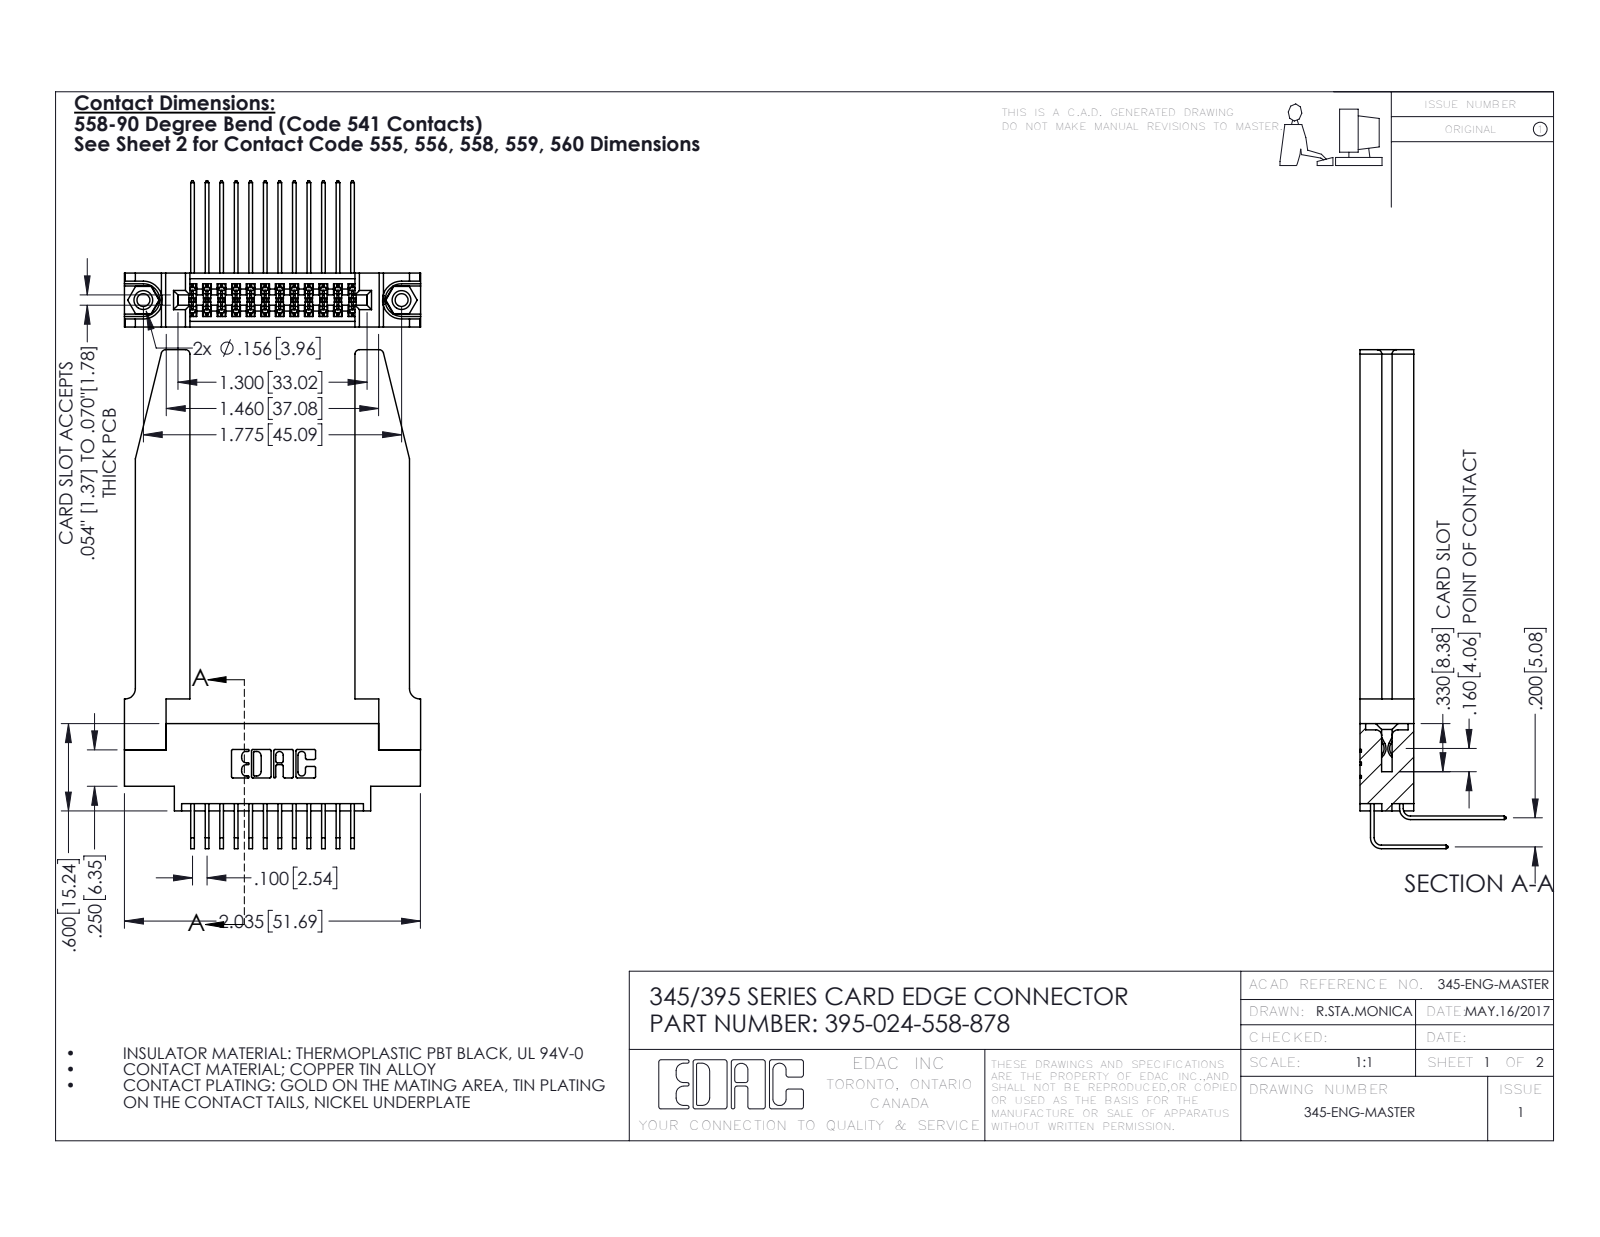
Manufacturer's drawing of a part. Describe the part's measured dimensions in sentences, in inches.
The part is named "345-220-078_345-220-078; 345 Part_0.170 Offset - 0.156 Dia-TH; 345-250-001_345-250-001-102; 345-292-001_558 Tail - 2 (+2 more)". Its 3-D file was written by "SolidWorks 2016 (CONFIG_CONTROL_DESIGN)". It is 29 solids with 1612 faces: 1066 planar, 494 cylindrical and 52 other. Overall it measures 3.429 by 2.036 by 1.005 inches. Its volume is 0.765 cubic inches and its surface area 21.86 square inches. Round holes: 2 of diameter 0.089, 2 of diameter 0.125, 2 of diameter 0.156, 1 of diameter 0.064. Round bosses or shafts: 2 of diameter 0.155. Partial cylindrical surfaces (rounded edges, fillets, slot ends): 37 of radius 0.006, 22 of radius 0.01, 8 of radius 0.03, 6 of radius 0.007, 6 of radius 0.031, 3 of radius 0.026, 2 of radius 0.014, 2 of radius 0.019. The main face-to-face distances are 0.37, 0.072, 0.298, 0.2, 0.15, 0.148, 0.22, 0.077, 1.135, 0.098. The hole center spacings are 0.27, 1.543, 1.775.
